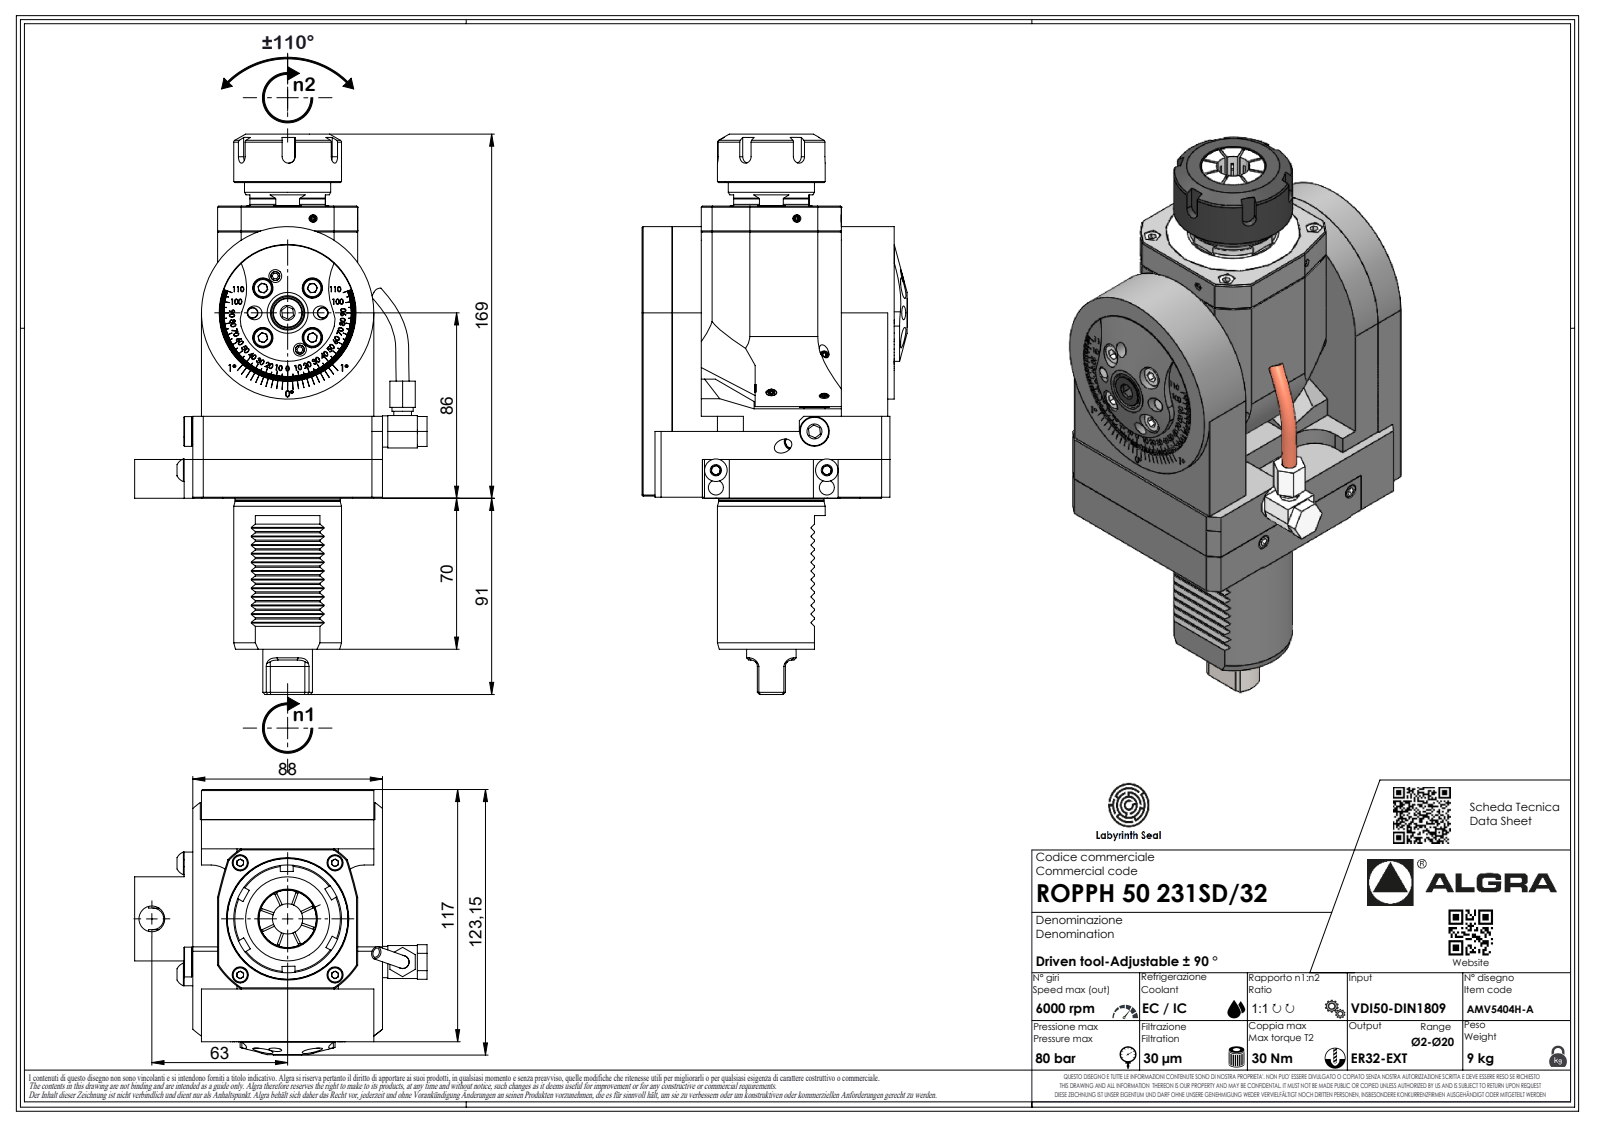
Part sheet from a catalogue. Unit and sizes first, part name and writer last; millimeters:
Units: millimetres
Overall size (bounding box): 259.91 × 135.7 × 123
Round holes (diameter × count): ⌀2.1 ×1
Round bosses / shafts (diameter × count): ⌀80 ×1, ⌀50 ×1, ⌀48.7 ×1, ⌀40 ×1, ⌀23 ×1, ⌀14.5 ×1, ⌀9.8 ×1, ⌀8.2 ×1
Partial cylindrical surfaces — rounded edges, fillets, slot ends (radius × count): R0.3 ×12, R3 ×11, R0.33 ×7, R0.52 ×7, R3.7 ×7, R10 ×2, R12 ×2, R28 ×2
Main face-to-face distances: 4, 84, 65, 0.5, 76.5, 11.5, 7.5, 27.5, 88, 24.5
Volume: 1 246 000 mm³ · Surface area: 109 444 mm²
Bodies: 2 solids, 649 faces (399 planar, 97 cylindrical, 153 other)
Part name (STEP PRODUCT): ROPPH50231SD32
STEP written by: SolidWorks 2023 (AUTOMOTIVE_DESIGN)
